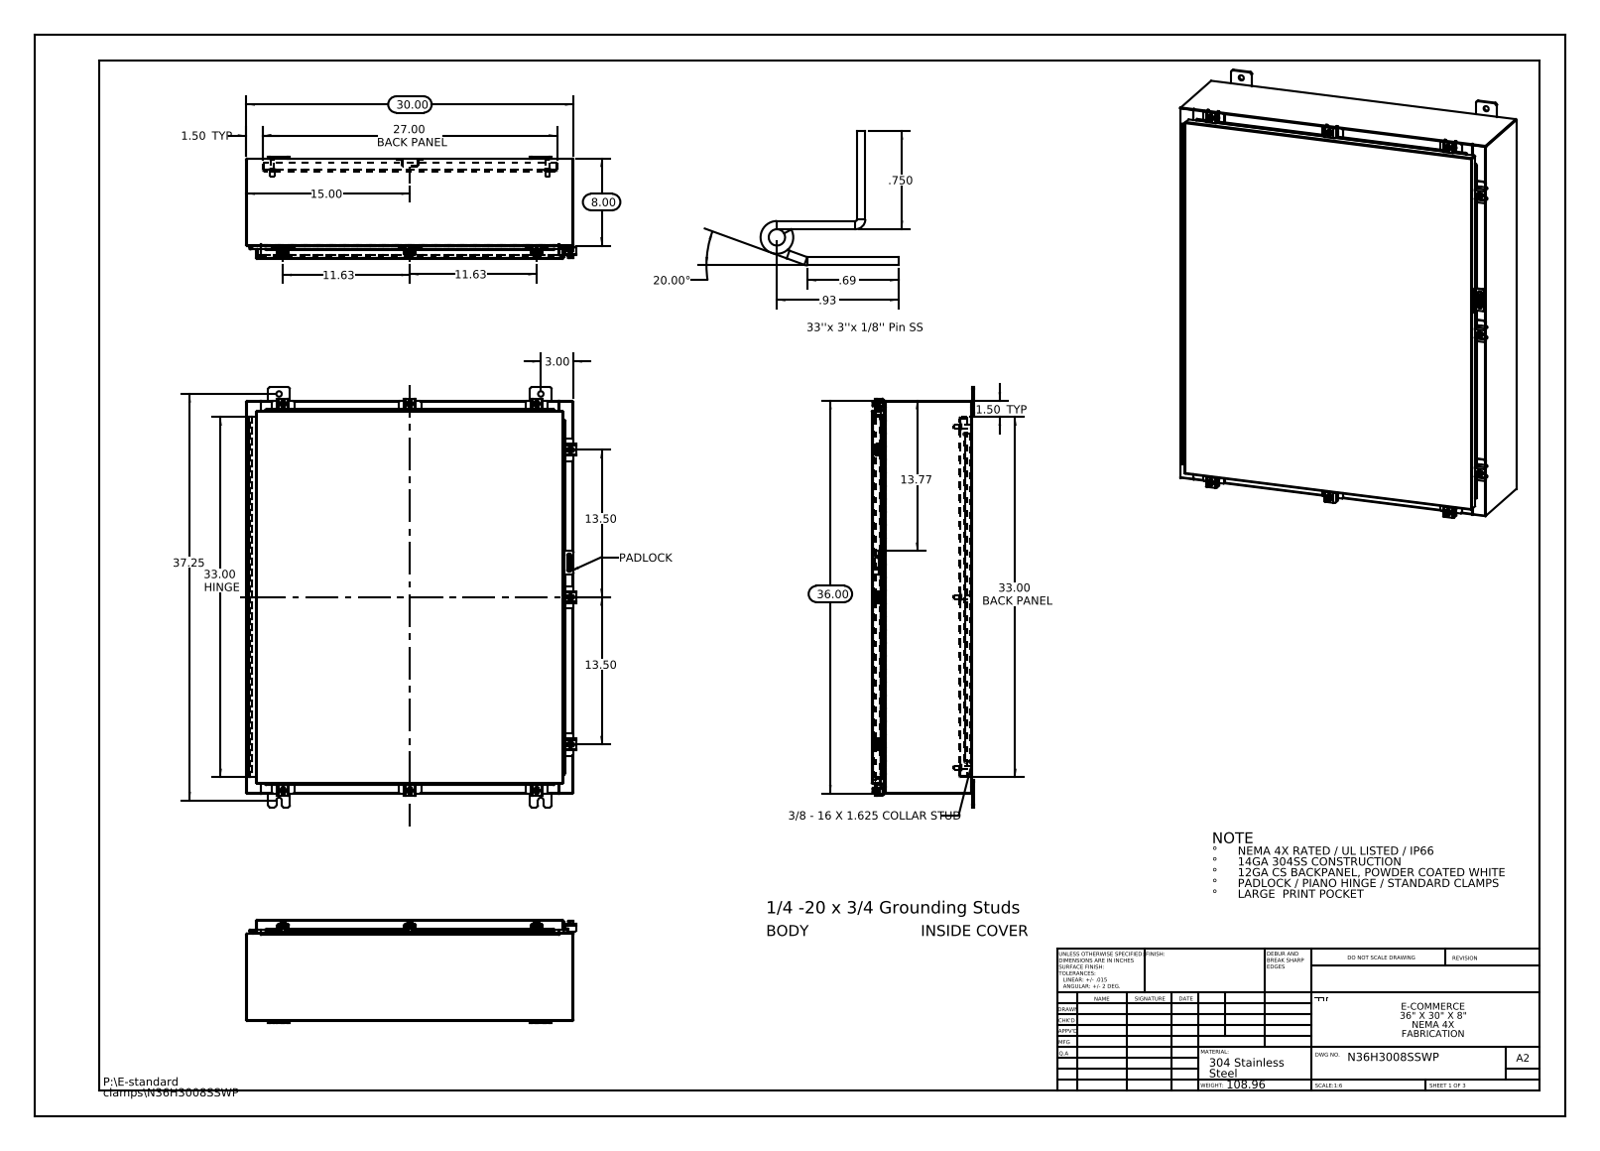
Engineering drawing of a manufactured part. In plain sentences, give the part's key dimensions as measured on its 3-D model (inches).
The part is named "N36H3008SSWP Mounting Studs; N36H3008SSWP Body; N36H3008SSWP Standard Clamps; N36H3008SSWP 22101002 (+8 more)". Its 3-D file was written by "SolidWorks 2013 (CONFIG_CONTROL_DESIGN)". It is 65 solids with 2456 faces: 1288 planar, 1028 cylindrical and 140 other. Overall it measures 38.5 by 30.211 by 9.389 inches. Its volume is 382.5 cubic inches and its surface area 9 518 square inches. Round holes: 10 of diameter 0.5, 9 of diameter 0.213, 9 of diameter 0.26, 2 of diameter 0.125, 1 of diameter 0.125. Round bosses or shafts: 10 of diameter 0.25, 9 of diameter 0.5, 9 of diameter 0.399, 6 of diameter 0.625, 6 of diameter 0.375, 6 of diameter 0.33. Partial cylindrical surfaces (rounded edges, fillets, slot ends): 42 of radius 0.06, 31 of radius 0.013, 25 of radius 0.088, 24 of radius 0.19, 18 of radius 0.12, 18 of radius 0.141, 13 of radius 0.05, 12 of radius 0.08. The main face-to-face distances are 0.075, 9.126, 9.051, 9.201, 0.104, 1, 8.126, 1.075, 8.051, 1.179. The hole center spacings are 15.625, 17.754, 29.694, 33.366, 37.309, 25.25, 35.451, 1.858.
